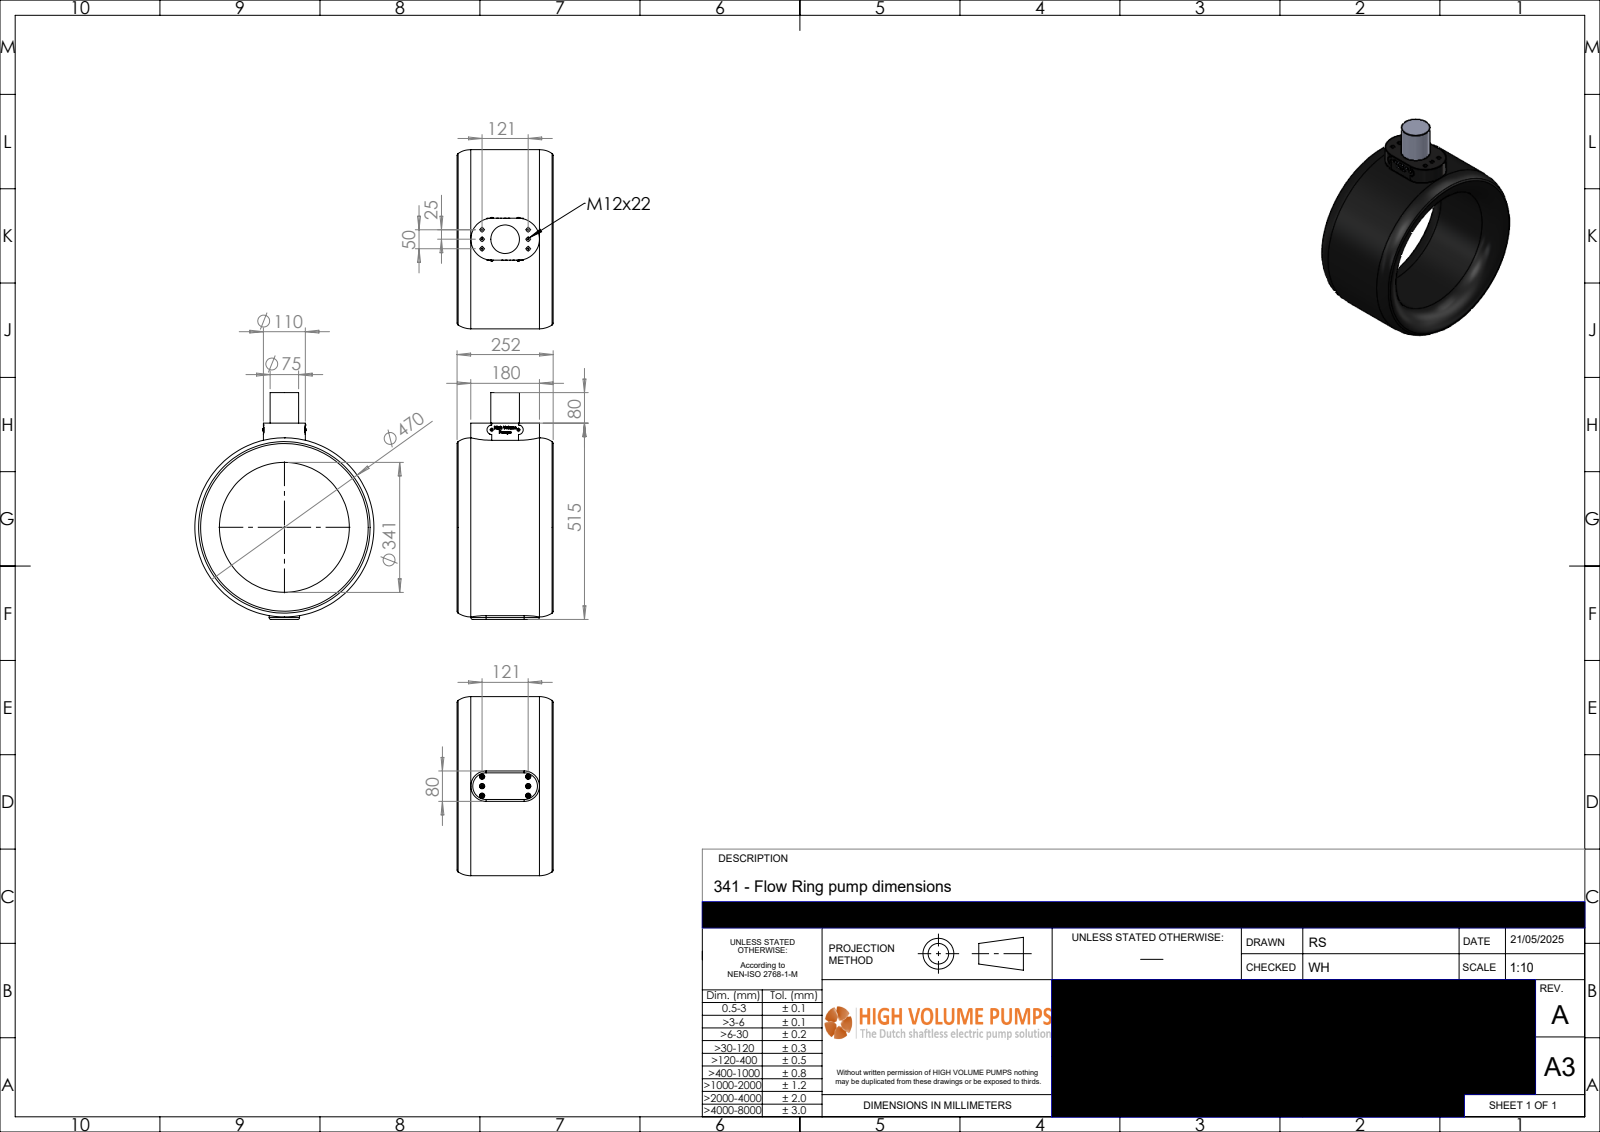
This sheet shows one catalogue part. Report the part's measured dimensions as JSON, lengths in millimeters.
{"part_name": "P-341-030-rev-A-FR", "step_written_by": "SolidWorks 2024 (AUTOMOTIVE_DESIGN)", "units": "millimeters", "bodies": {"solids": 1, "faces": 693, "planar": 389, "cylindrical": 56, "other": 248}, "overall_size": [595.04, 470, 252], "volume_mm3": 20210000, "surface_area_mm2": 784033, "round_holes": [[6.6, 6], [10.2, 6], [341, 1]], "round_bosses_or_shafts": [[11.57, 6], [6, 6], [7.6, 2], [470, 1], [75, 1]], "partial_cylinders_radius": [[5, 2], [12.5, 2], [40, 2], [54, 2], [55, 2]], "face_to_face_distances": [515.04, 80, 595.04, 110, 109, 0.5, 15, 95, 1, 14], "hole_center_spacings": [25, 123.56, 121, 50, 130.92]}
